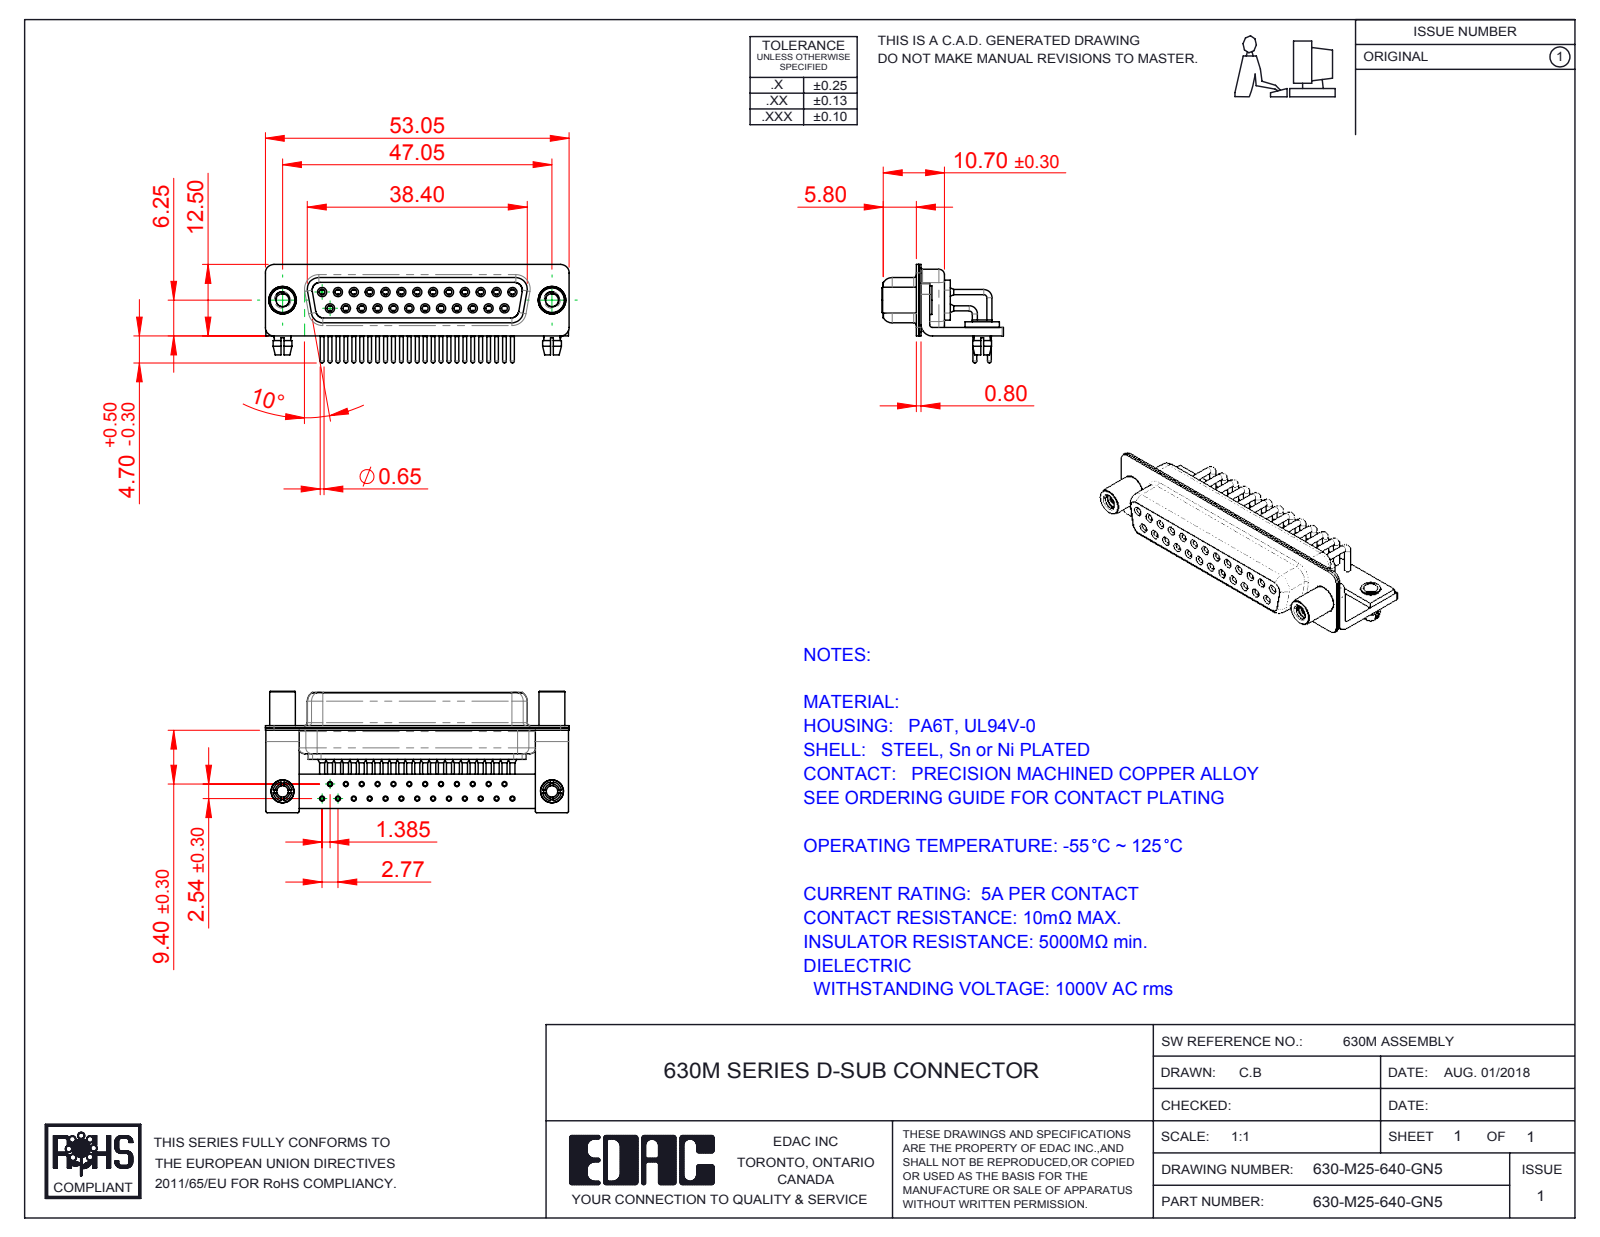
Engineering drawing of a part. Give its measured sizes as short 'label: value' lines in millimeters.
name: 630M Shell Rear_25 Contacts; 630M Stabilizer Board_25 Contacts; 630M Housing_25 Contacts; 630M Shell Front_25 Contacts (+6 more)
written by: SolidWorks 2016 (CONFIG_CONTROL_DESIGN)
unit: mm
bodies: 35 solids, 1846 faces (518 planar, 858 cylindrical, 470 other)
size: 53.05 × 21.2 × 17.2
volume: 4 624 mm³; area: 11 662 mm²
holes: 27× ⌀2, 25× ⌀0.9, 25× ⌀1, 25× ⌀1.1, 25× ⌀1.7, 25× ⌀1.8, 2× ⌀2.26, 2× ⌀2.5, 2× ⌀3.2, 2× ⌀4, 2× ⌀4.8
bosses: 25× ⌀1.6, 25× ⌀1.5, 25× ⌀0.9, 25× ⌀0.65, 2× ⌀5, 2× ⌀4.9, 2× ⌀4.5, 2× ⌀4
rounds: 16× R0.25, 16× R1.5, 13× R2, 10× R1.35, 8× R1.6, 5× R0.5, 4× R0.6, 4× R0.65
face distances: 0.4, 2.3, 1.9, 9.35, 1.45, 8.95, 0.85, 0.8, 6.2, 1
hole spacings: 2.77, 5.54, 8.31, 11.08, 13.85, 3.16, 4.87, 16.62
